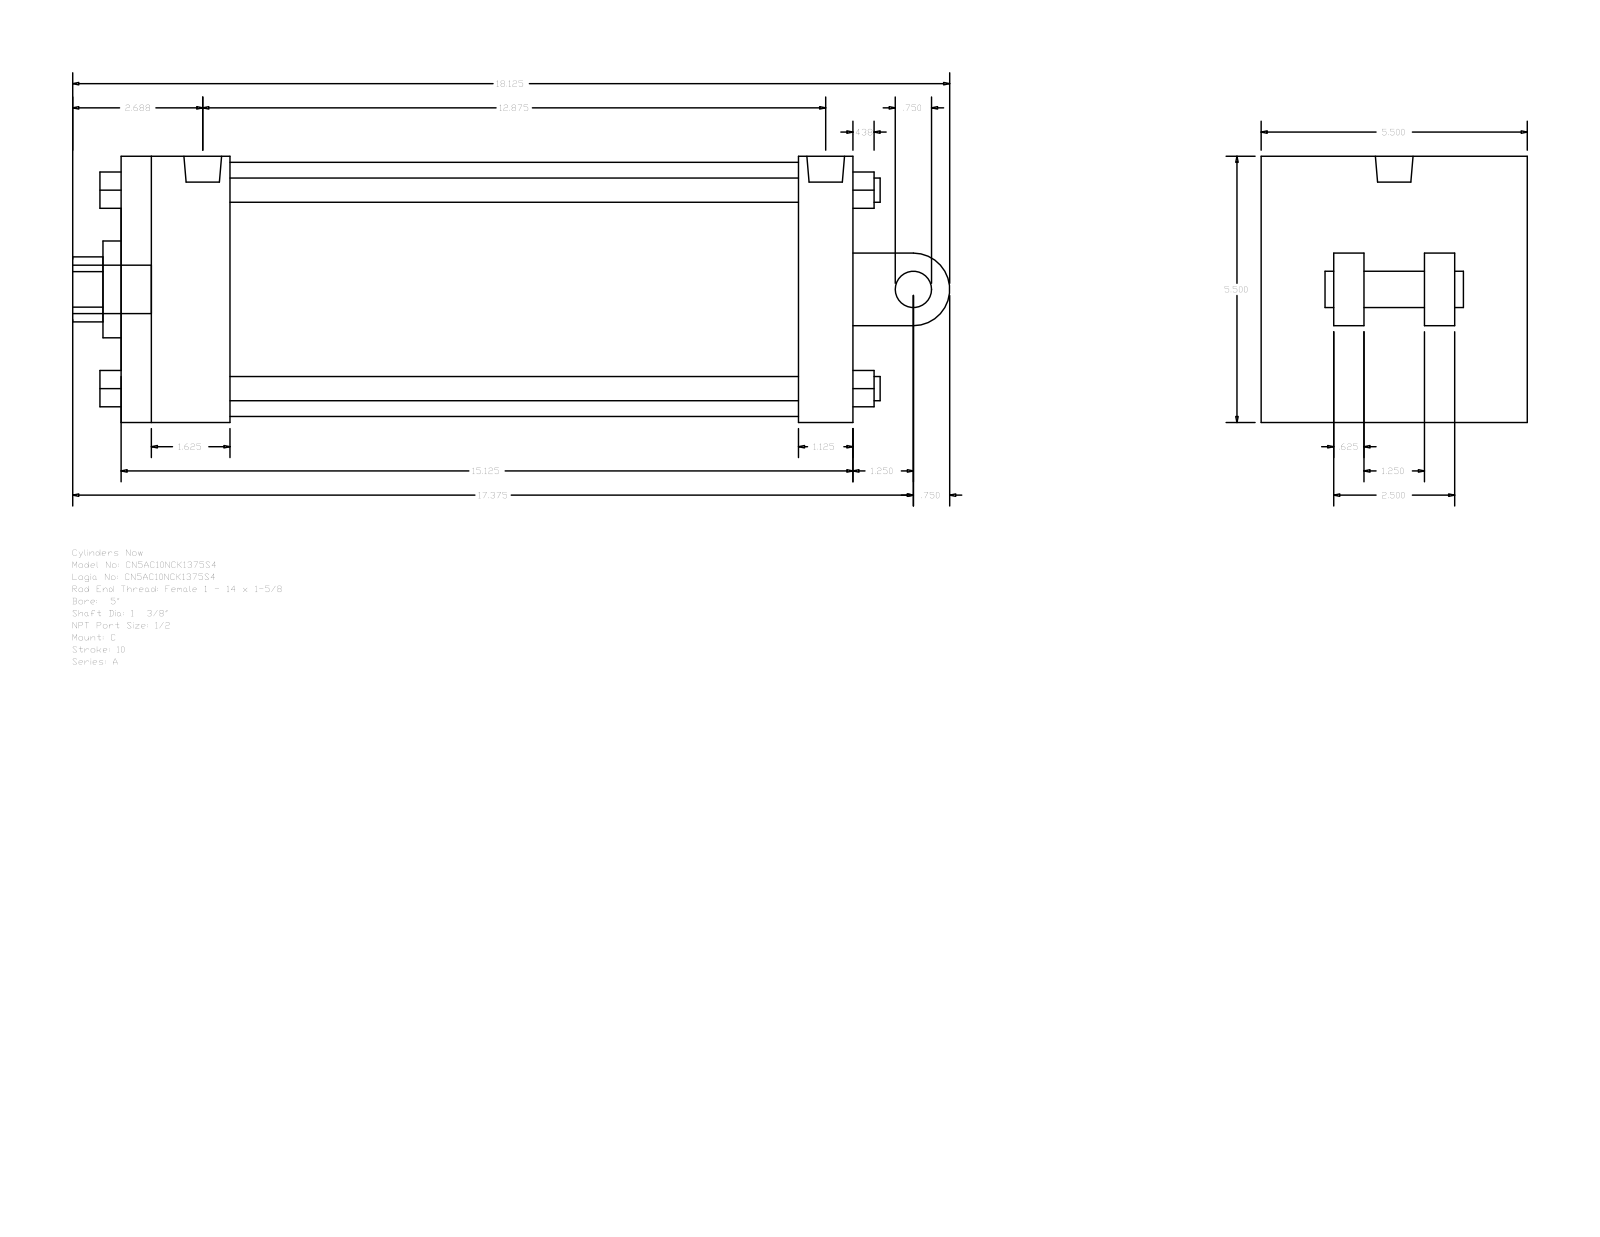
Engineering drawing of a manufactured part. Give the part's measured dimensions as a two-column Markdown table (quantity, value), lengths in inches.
| quantity | value |
| --- | --- |
| part name | A_C__0500_1.375 |
| STEP written by | GSSL Pune (CONFIG_CONTROL_DESIGN) |
| units | inches |
| bodies | 0 solids, 135 faces (102 planar, 33 cylindrical, 0 other) |
| overall size | 18.125 × 5.5 × 5.5 |
| round holes (diameter × count) | 0.344 × 2, 0.778 × 1, 1.375 × 1, 2 × 1, 5.25 × 1 |
| round bosses / shafts (diameter × count) | 0.5 × 4, 0.344 × 2, 1 × 1, 0.778 × 1, 0.75 × 1 |
| partial cylindrical surfaces (radius × count) | 0.672 × 1, 0.75 × 1 |
| main face-to-face distances | 5.5, 15.125, 1.125, 2.25, 14, 11.75, 12.875, 1.5, 0.625, 4 |
| hole center spacings | 0.094 |
